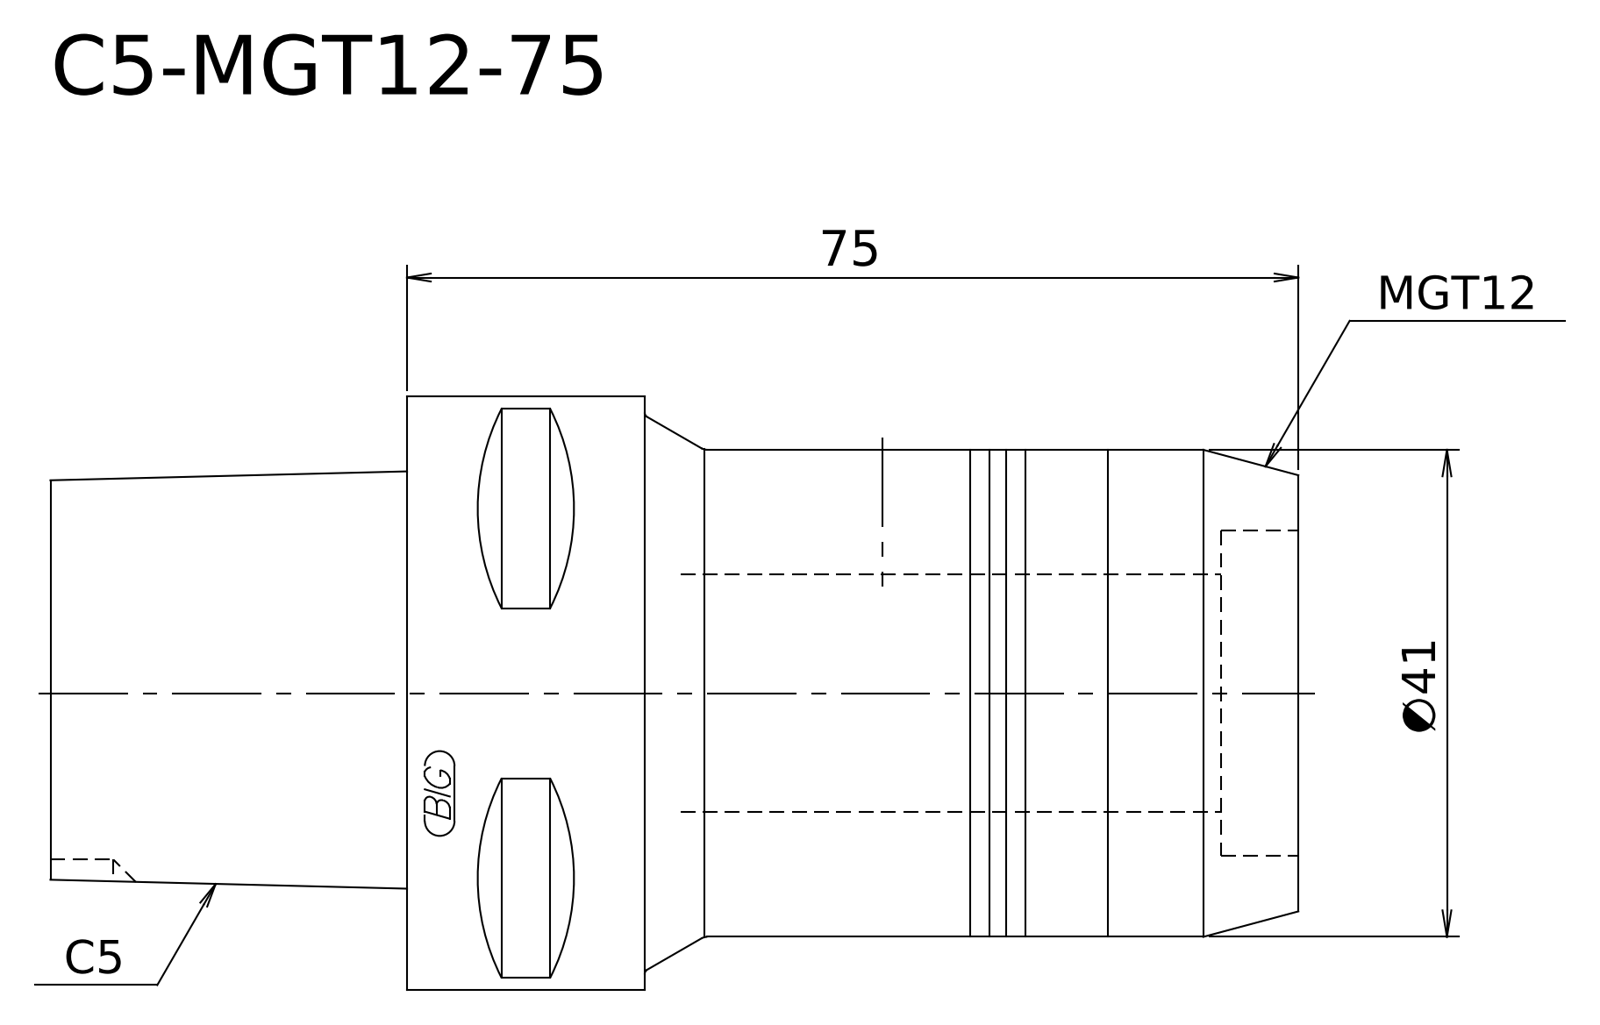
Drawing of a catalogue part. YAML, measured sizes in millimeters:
step_written_by: "Kubotek KeyCreator V8.5.1 (14335) (CONFIG_CONTROL_DESIGN)"
units: millimeters
bodies: {solids: 1, faces: 9, planar: 4, cylindrical: 2, other: 3}
overall_size: [105, 49.98, 49.98]
volume: 138952
surface_area: 16783
round_bosses_or_shafts:
  - {diameter: 49.98, count: 1}
  - {diameter: 41, count: 1}
face_to_face_distances: [75, 105, 30, 55, 20, 50]
